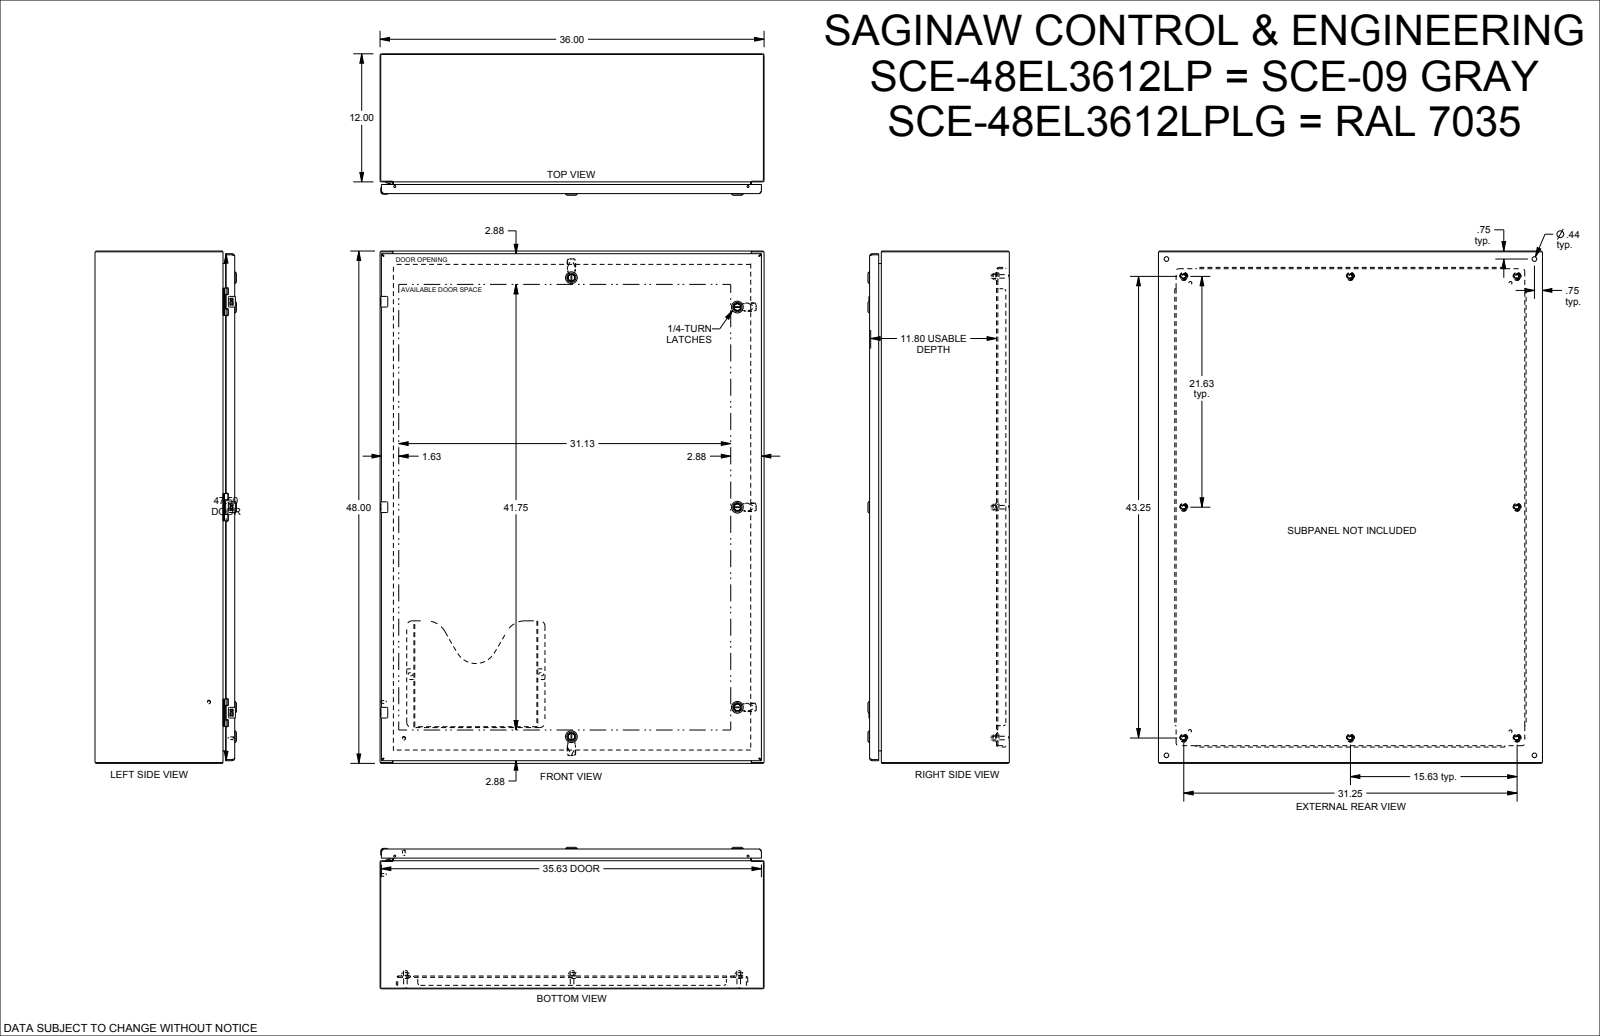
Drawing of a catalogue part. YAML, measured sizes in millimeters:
part_name: "SCE-48EL3612LPLG"
step_written_by: "SolidWorks 2019 (CONFIG_CONTROL_DESIGN)"
units: millimeters
bodies: {solids: 0, faces: 4768, planar: 2330, cylindrical: 1319, other: 1119}
overall_size: [1219.2, 914.4, 336.7]
round_holes:
  - {diameter: 9.3, count: 8}
  - {diameter: 12.7, count: 8}
  - {diameter: 4.4, count: 6}
  - {diameter: 5.2, count: 6}
  - {diameter: 6.2, count: 6}
  - {diameter: 6.8, count: 6}
  - {diameter: 9.5, count: 6}
  - {diameter: 5, count: 5}
  - {diameter: 8, count: 5}
  - {diameter: 10, count: 5}
  - {diameter: 16.1, count: 5}
  - {diameter: 7.1, count: 4}
round_bosses_or_shafts:
  - {diameter: 4.3, count: 9}
  - {diameter: 9.3, count: 8}
  - {diameter: 8.4, count: 8}
  - {diameter: 6.4, count: 6}
  - {diameter: 6.1, count: 6}
  - {diameter: 28, count: 5}
  - {diameter: 22, count: 5}
  - {diameter: 20.4, count: 5}
partial_cylinders:
  - {radius: 0.3, count: 136}
  - {radius: 0.3, count: 52}
  - {radius: 0.5, count: 52}
  - {radius: 0.4, count: 32}
  - {radius: 4, count: 20}
  - {radius: 1, count: 17}
  - {radius: 0.6, count: 16}
  - {radius: 2.5, count: 16}
face_to_face_distances: [1.9, 2.6, 328.2, 330.1, 332.7, 330.8, 28.6, 299.6, 25.4, 302.8]
hole_center_spacings: [489, 977.9, 1.3, 12.5, 12.5, 25, 463.9, 476.4]
